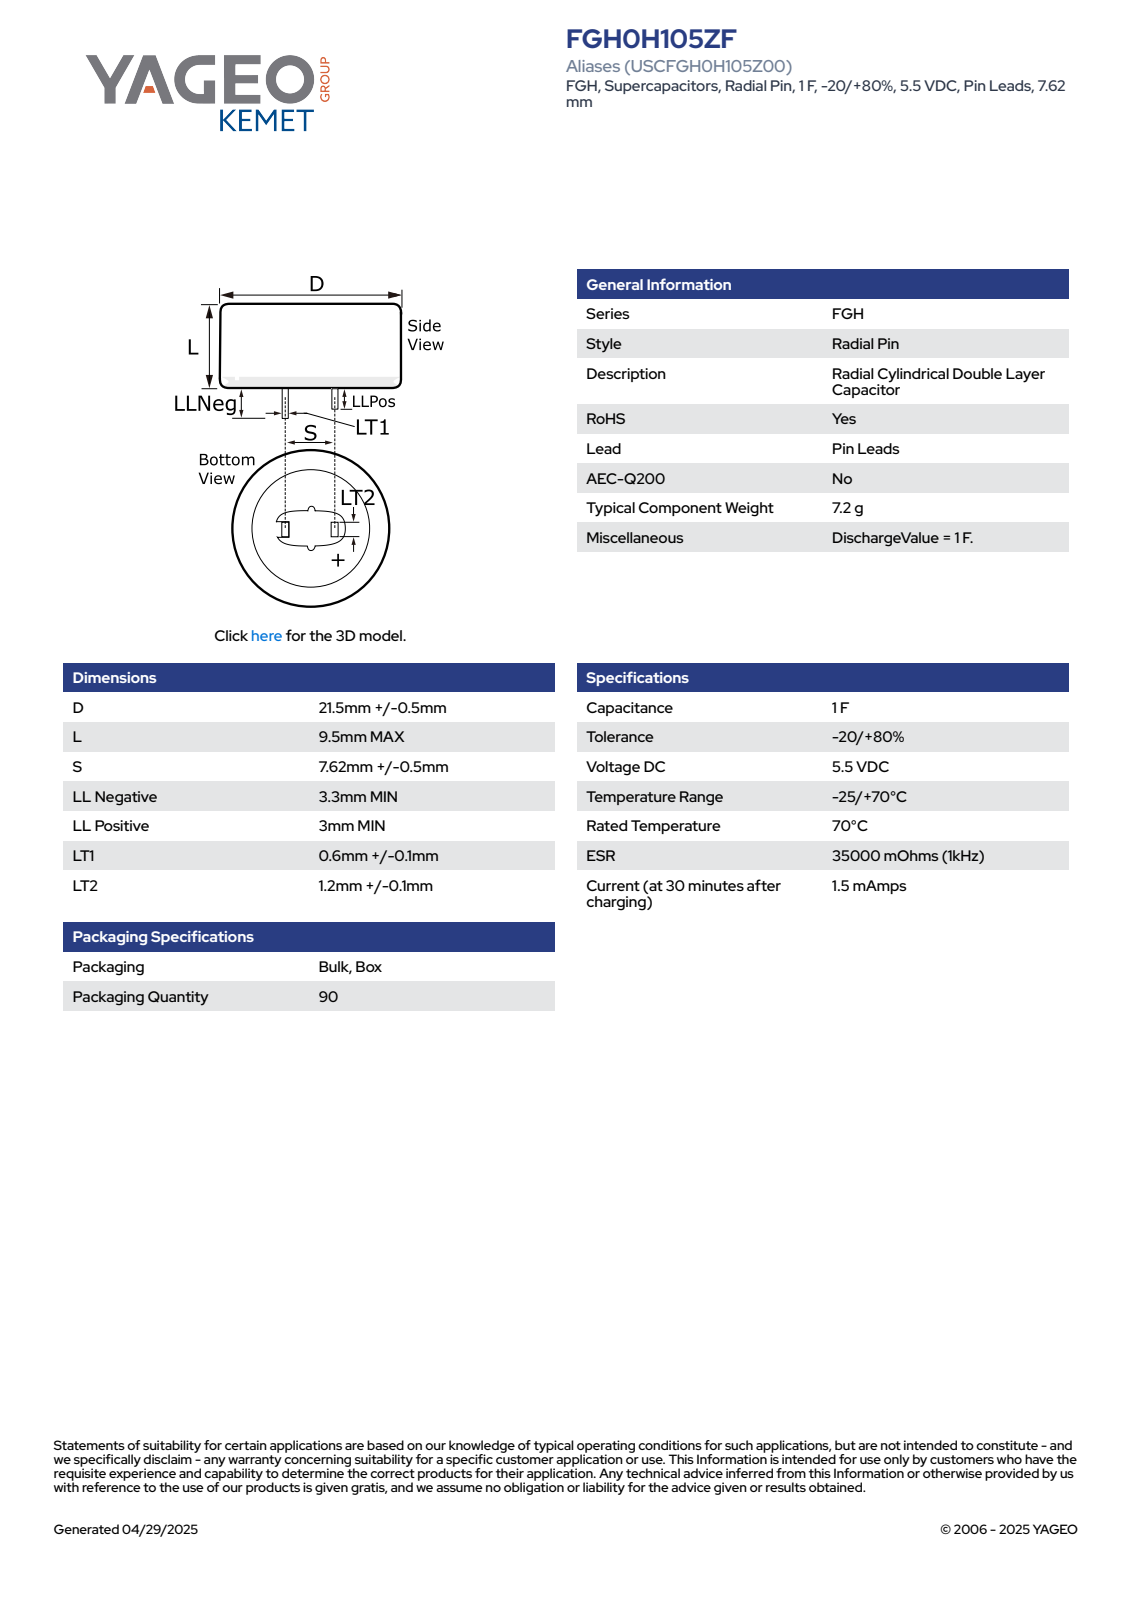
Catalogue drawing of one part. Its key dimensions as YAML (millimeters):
part_name: "CDR_LPLLN_D22L9.5S7.62LLNEG3.3LLPOS3LT10.7LT21.3"
step_written_by: "SolidWorks 2014 (AUTOMOTIVE_DESIGN)"
units: millimeters
bodies: {solids: 1, faces: 78, planar: 70, cylindrical: 4, other: 4}
overall_size: [22, 22, 12.8]
volume: 3606
surface_area: 1406
round_bosses_or_shafts:
  - {diameter: 22, count: 1}
partial_cylinders:
  - {radius: 11.01, count: 1}
face_to_face_distances: [9.5, 9.49, 0.7, 7.62, 1.3, 8.32, 6.92, 3, 12.49, 12.5]
